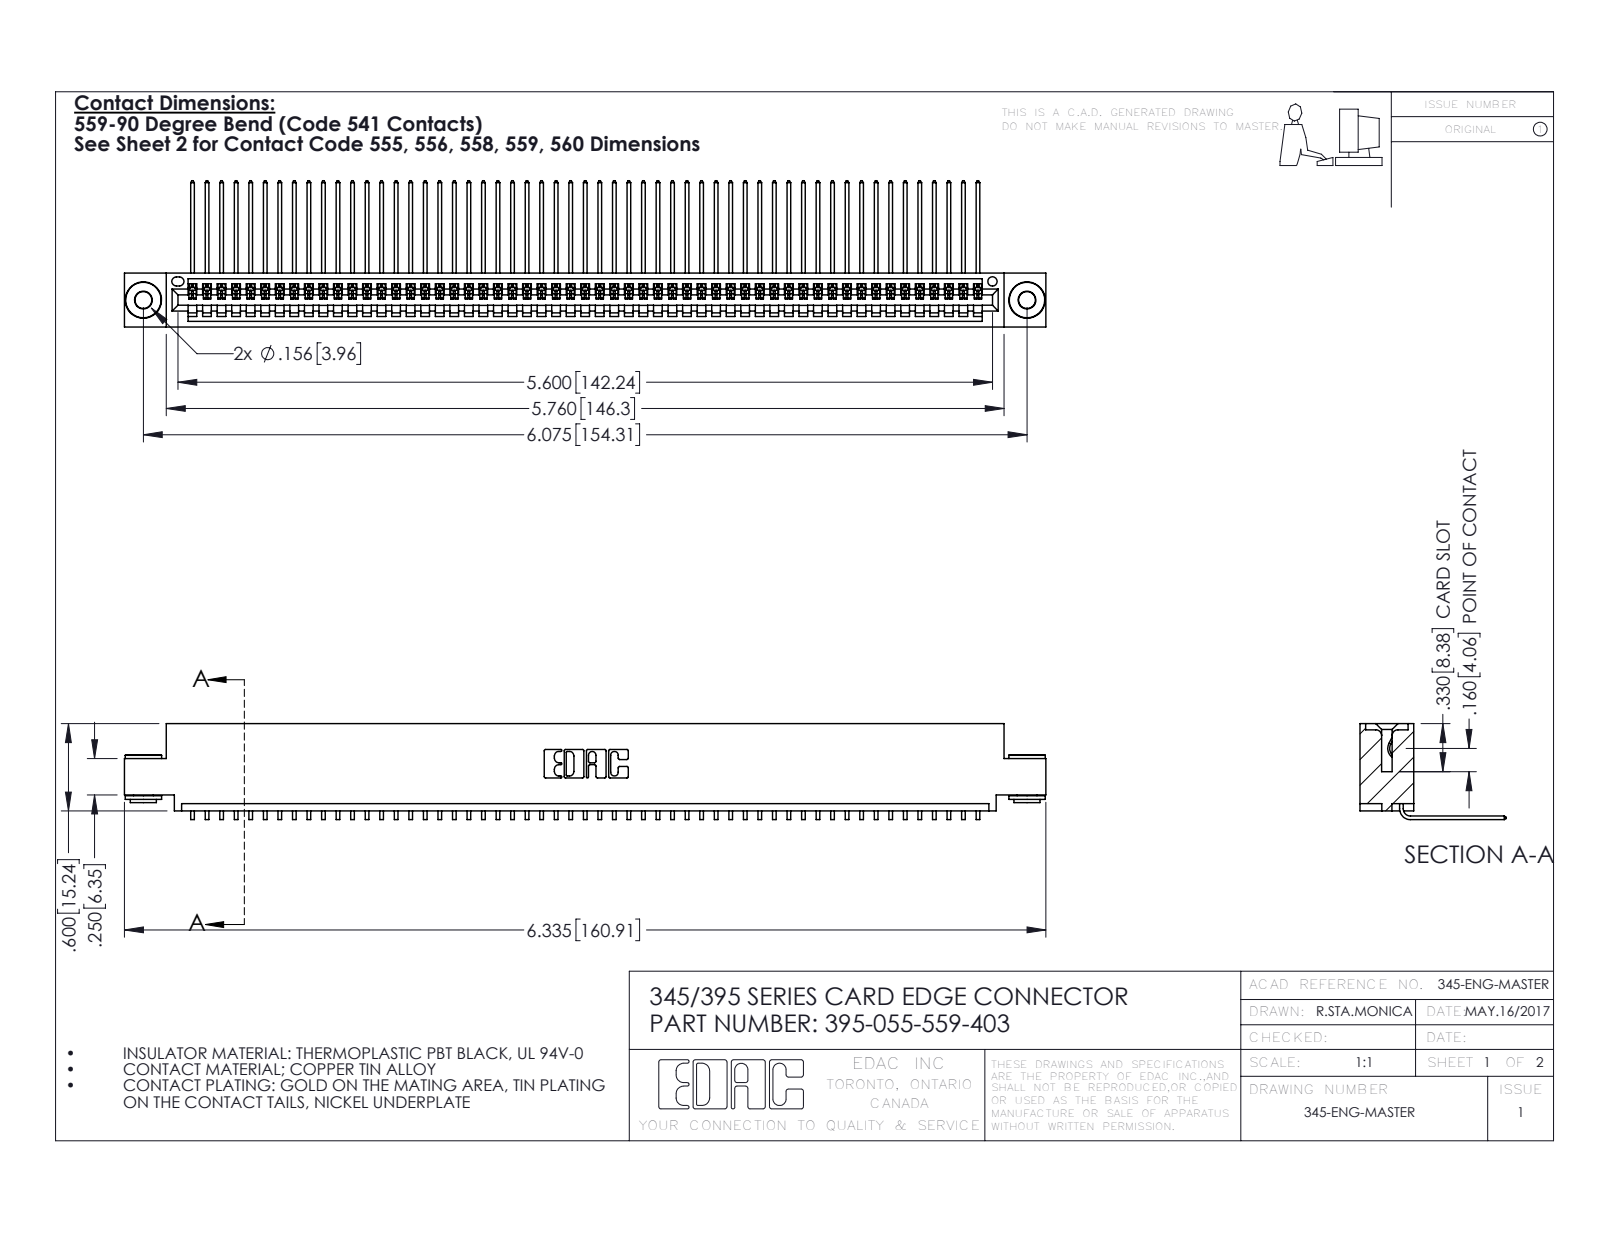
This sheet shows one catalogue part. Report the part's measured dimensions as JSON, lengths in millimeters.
{"part_name": "345-292-001_558 559 Tail - 1; 345-250-002_345-250-002-102; 345 Part_0.110 Offset - 0.156 Dia-TH; 395-055-559-403", "step_written_by": "SolidWorks 2016 (CONFIG_CONTROL_DESIGN)", "units": "millimeters", "bodies": {"solids": 58, "faces": 3468, "planar": 2404, "cylindrical": 1056, "other": 8}, "overall_size": [160.9, 25.5, 16.7], "volume_mm3": 15500, "surface_area_mm2": 22170, "round_holes": [[2.9, 2], [4, 2], [1.6, 1]], "round_bosses_or_shafts": [[6.4, 2], [4.6, 2], [3.5, 2]], "partial_cylinders_radius": [[0.2, 110], [0.3, 22], [0.2, 6], [0.8, 6], [0.7, 3], [0.8, 2], [1, 2], [0.4, 1]], "face_to_face_distances": [1.8, 7.6, 9.4, 5.1, 0.6, 2.5, 6.9, 5.7, 3.8, 1.8], "hole_center_spacings": [6.9, 148.3, 154.3]}
